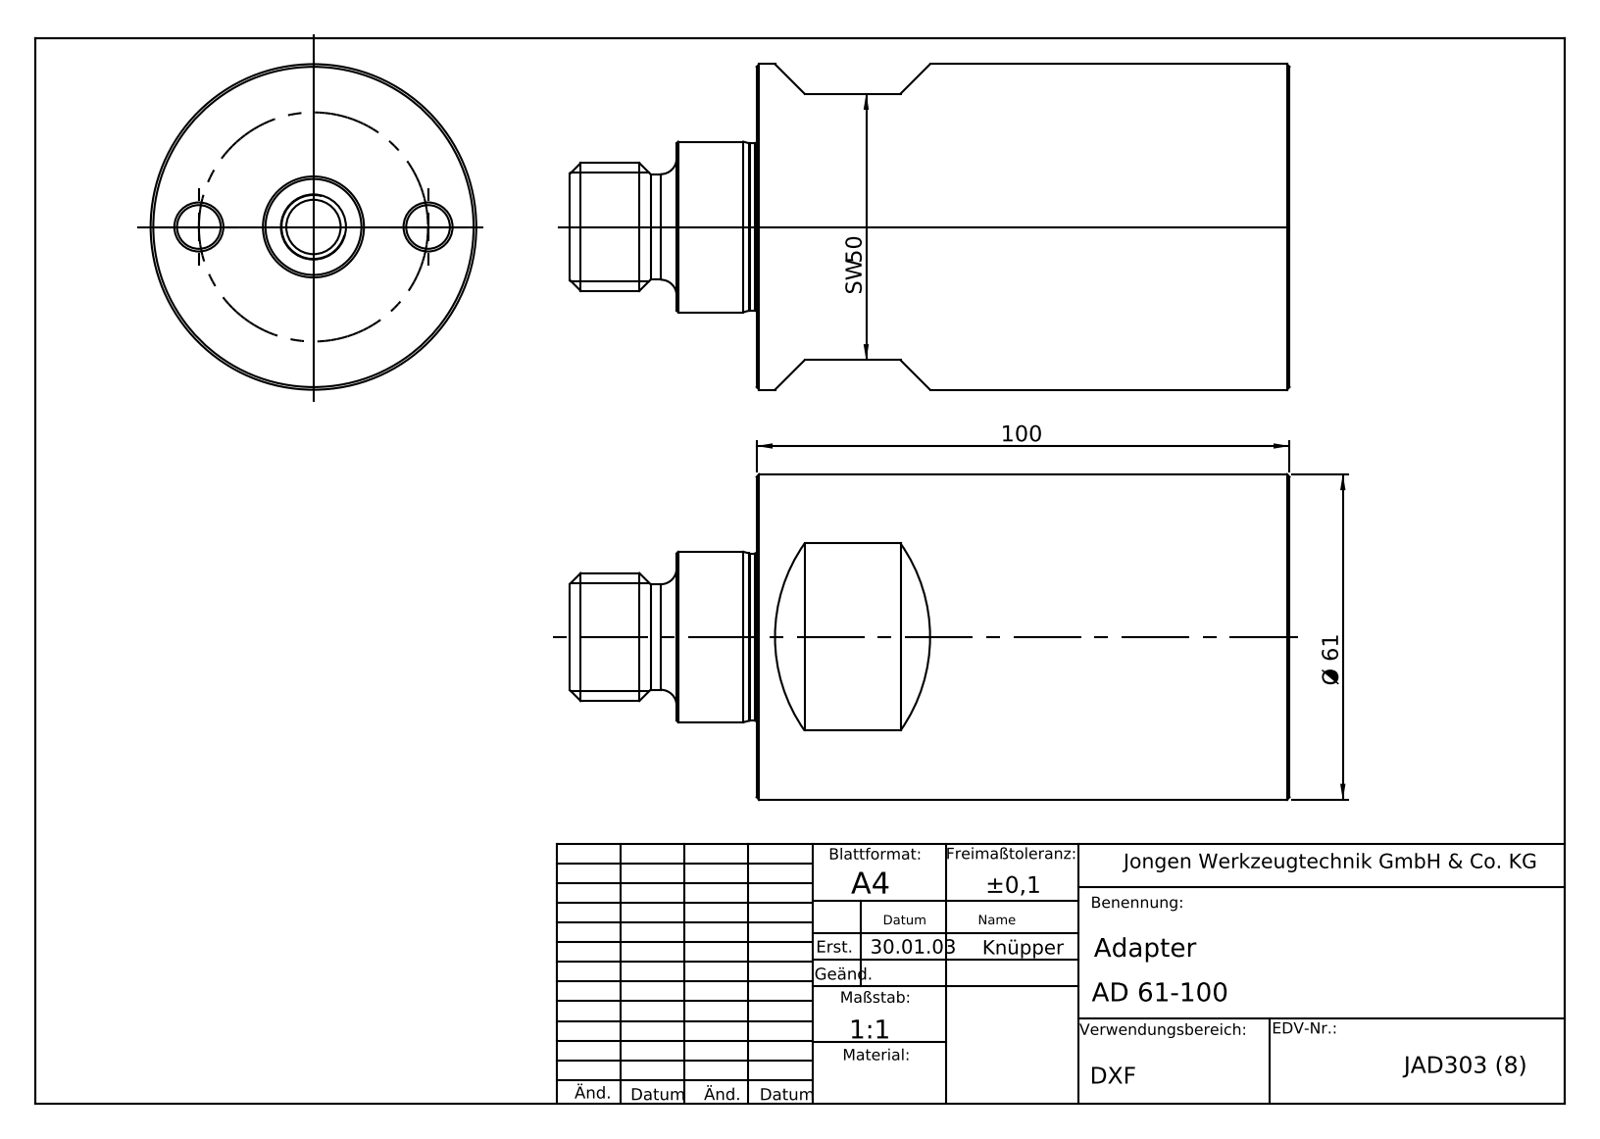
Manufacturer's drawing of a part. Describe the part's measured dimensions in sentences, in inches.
The part is named "AD 61-100". Its 3-D file was written by "SolidWorks 2014 (AUTOMOTIVE_DESIGN)". It is 1 solid with 42 faces: 11 planar, 11 cylindrical and 20 other. Overall it measures 5.315 by 2.406 by 2.406 inches. Its volume is 18.38 cubic inches and its surface area 46.8 square inches. Round holes: 2 of diameter 0.323, 1 of diameter 0.124, 1 of diameter 0.402, 1 of diameter 0.701, 1 of diameter 0.717. Round bosses or shafts: 1 of diameter 2.406, 1 of diameter 1.268, 1 of diameter 1.236, 1 of diameter 0.945, 1 of diameter 0.78. The main face-to-face distances are 3.937, 1.969, 0.891, 1.378, 5.315, 0.787, 0.591, 4.528, 5, 4.213. The hole center spacings are 0.846, 1.693.
